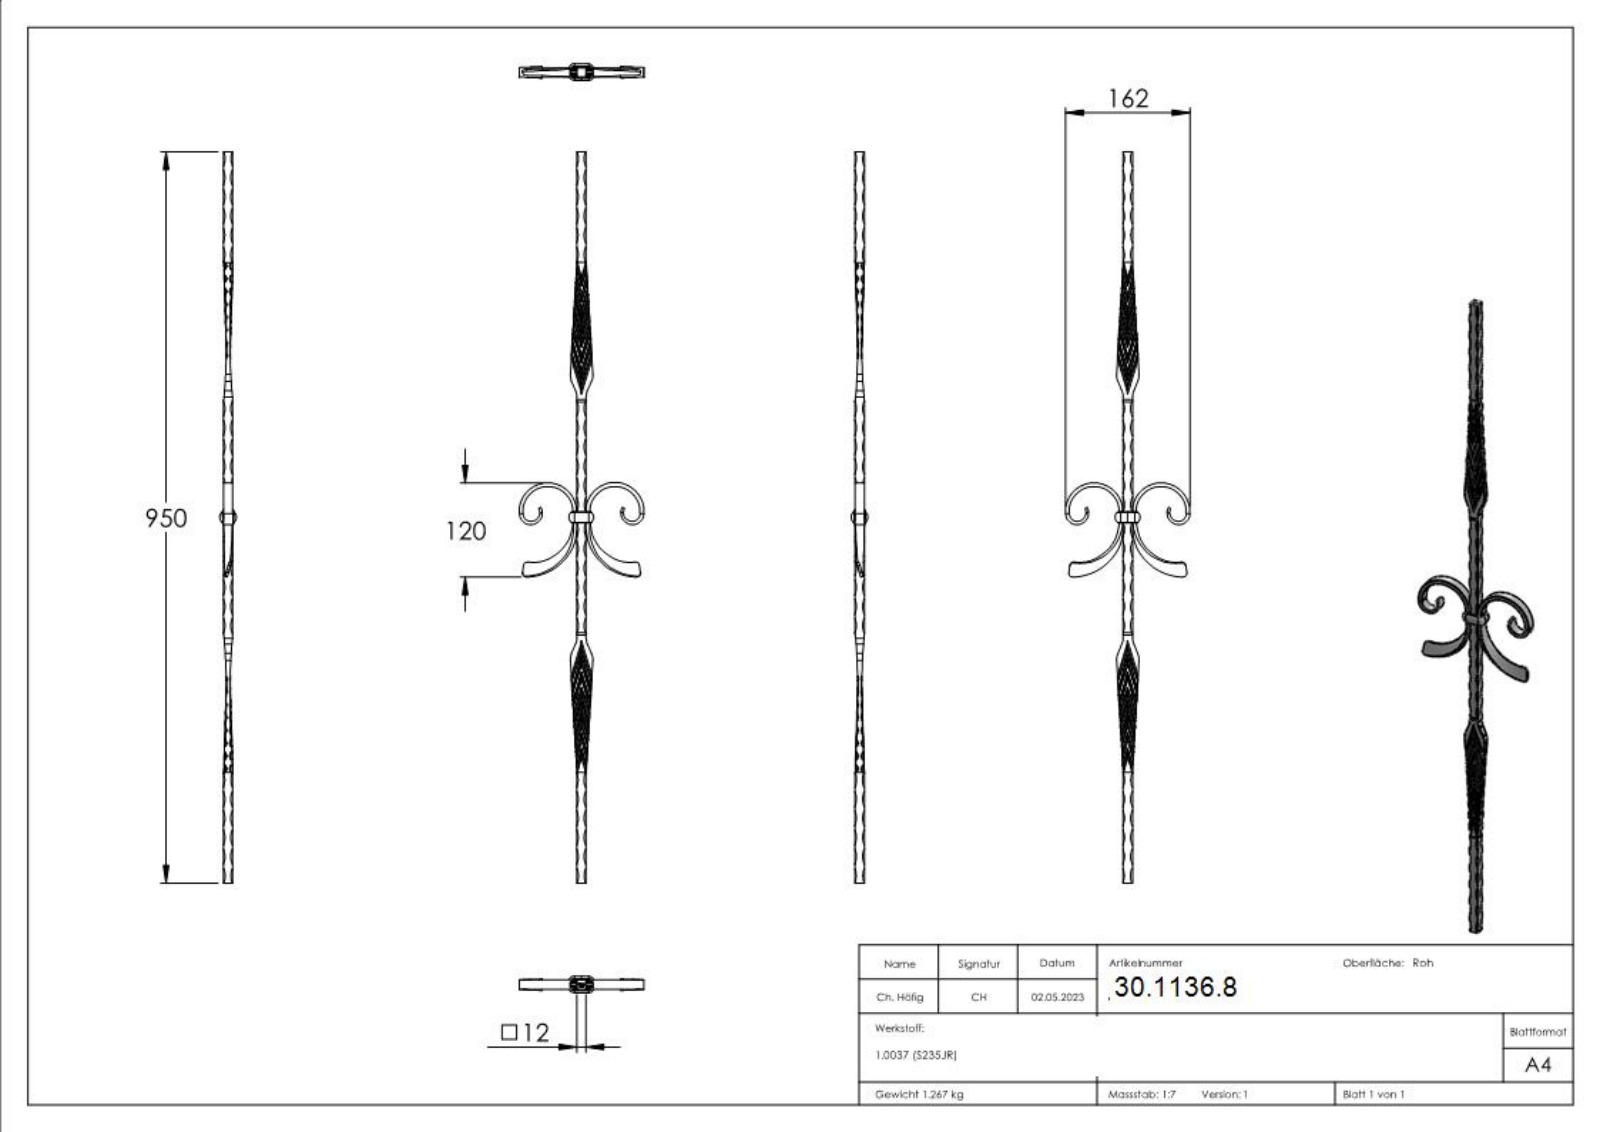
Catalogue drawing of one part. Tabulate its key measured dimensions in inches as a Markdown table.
| quantity | value |
| --- | --- |
| part name | 578-7 |
| STEP written by | SolidWorks 2018 (CONFIG_CONTROL_DESIGN) |
| units | inches |
| bodies | 1 solid, 1058 faces (478 planar, 239 cylindrical, 341 other) |
| overall size | 37.402 × 6.382 × 0.866 |
| volume | 9.91 in³ |
| surface area | 111.2 in² |
| partial cylindrical surfaces (radius × count) | 0.039 × 88, 0.008 × 80, 0.079 × 8, 0.787 × 8, 0.344 × 4, 1.181 × 4, 23.699 × 4, 1.28 × 2 |
| main face-to-face distances | 0.472, 0.16, 0.083, 0.32, 3.128, 0.076, 3.287, 0.243, 2.968, 2.037 |
